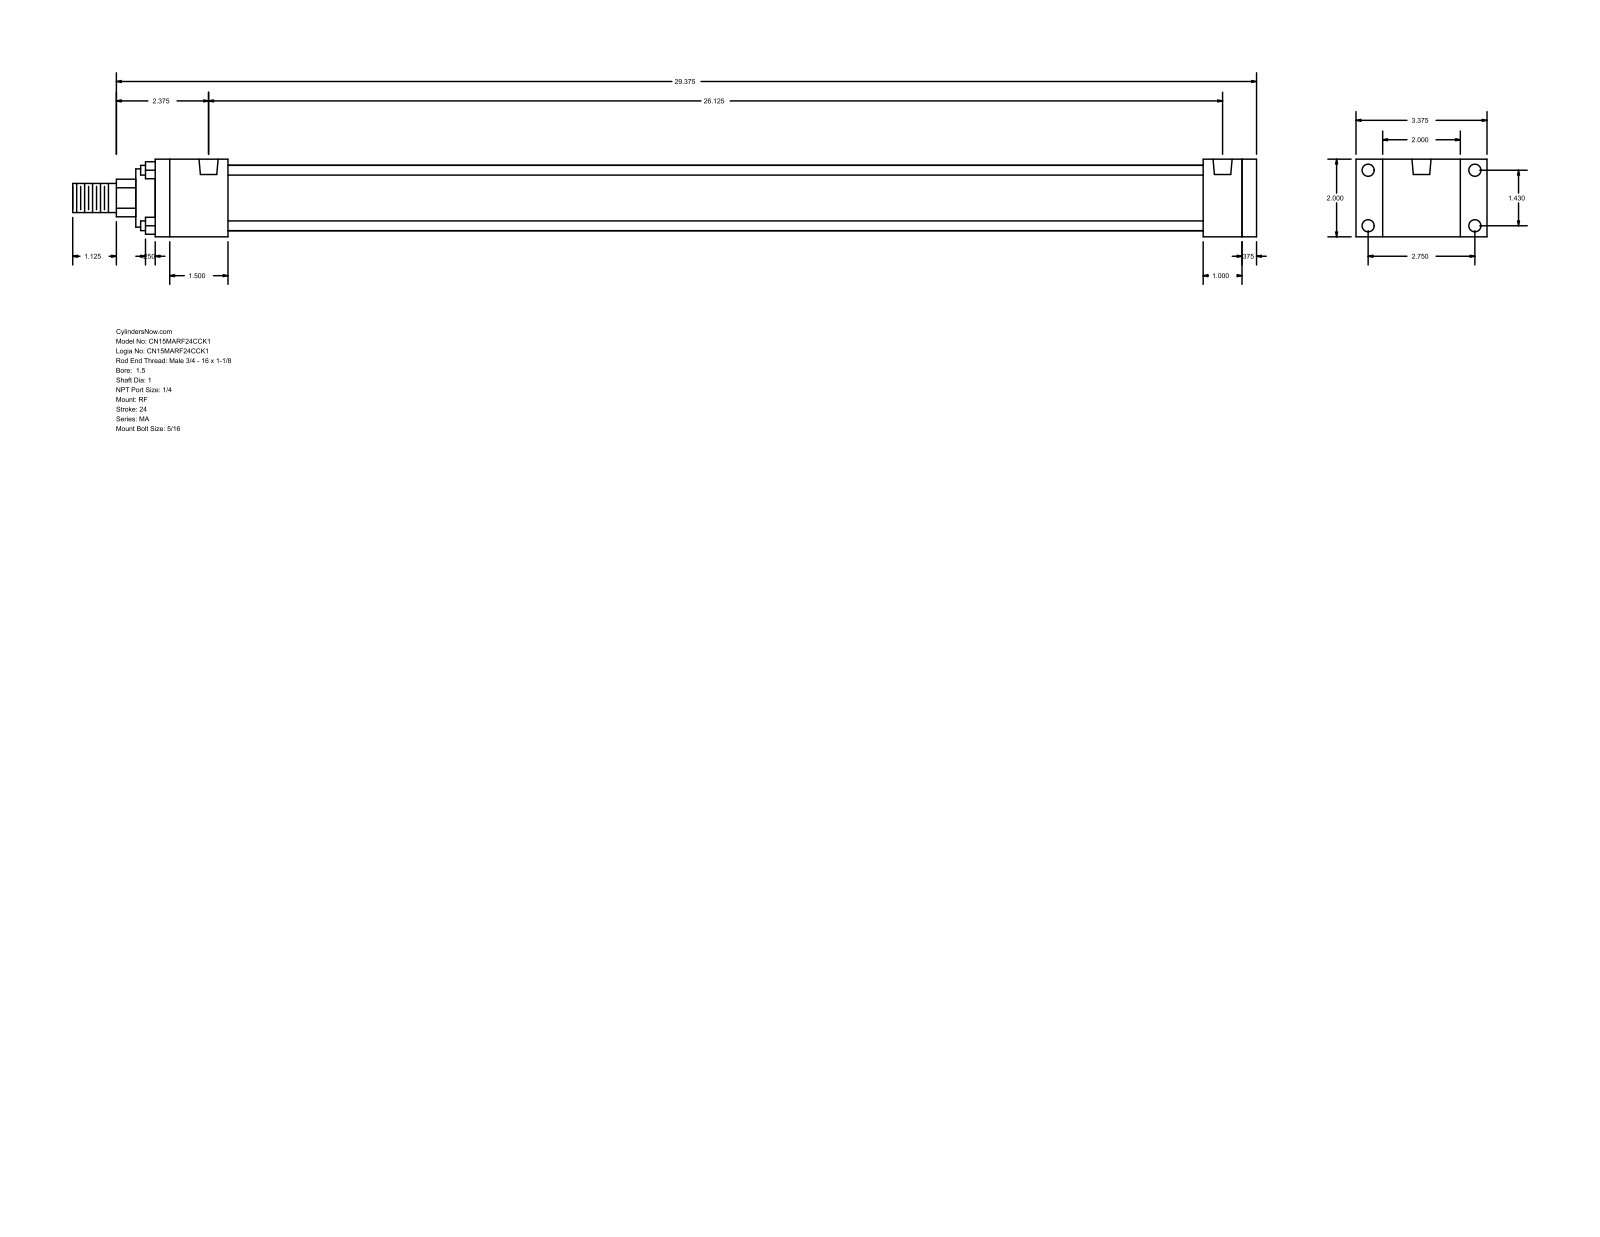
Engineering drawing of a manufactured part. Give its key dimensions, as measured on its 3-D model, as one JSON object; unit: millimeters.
{"part_name": "MA_RF__0150_1", "step_written_by": "GSSL Pune (CONFIG_CONTROL_DESIGN)", "units": "millimeters", "bodies": {"solids": 0, "faces": 92, "planar": 64, "cylindrical": 28, "other": 0}, "overall_size": [774.7, 85.72, 50.8], "round_holes": [[7.94, 8], [12.49, 2]], "round_bosses_or_shafts": [[6.35, 4], [42.93, 1], [38.1, 1], [25.4, 1], [19.05, 1]], "partial_cylinders_radius": [[12.29, 1]], "face_to_face_distances": [50.8, 9.52, 720.72, 711.2, 25.4, 685.8, 34.92, 47.63, 638.17, 663.57], "hole_center_spacings": [36.32, 69.84, 78.72, 663.57]}
